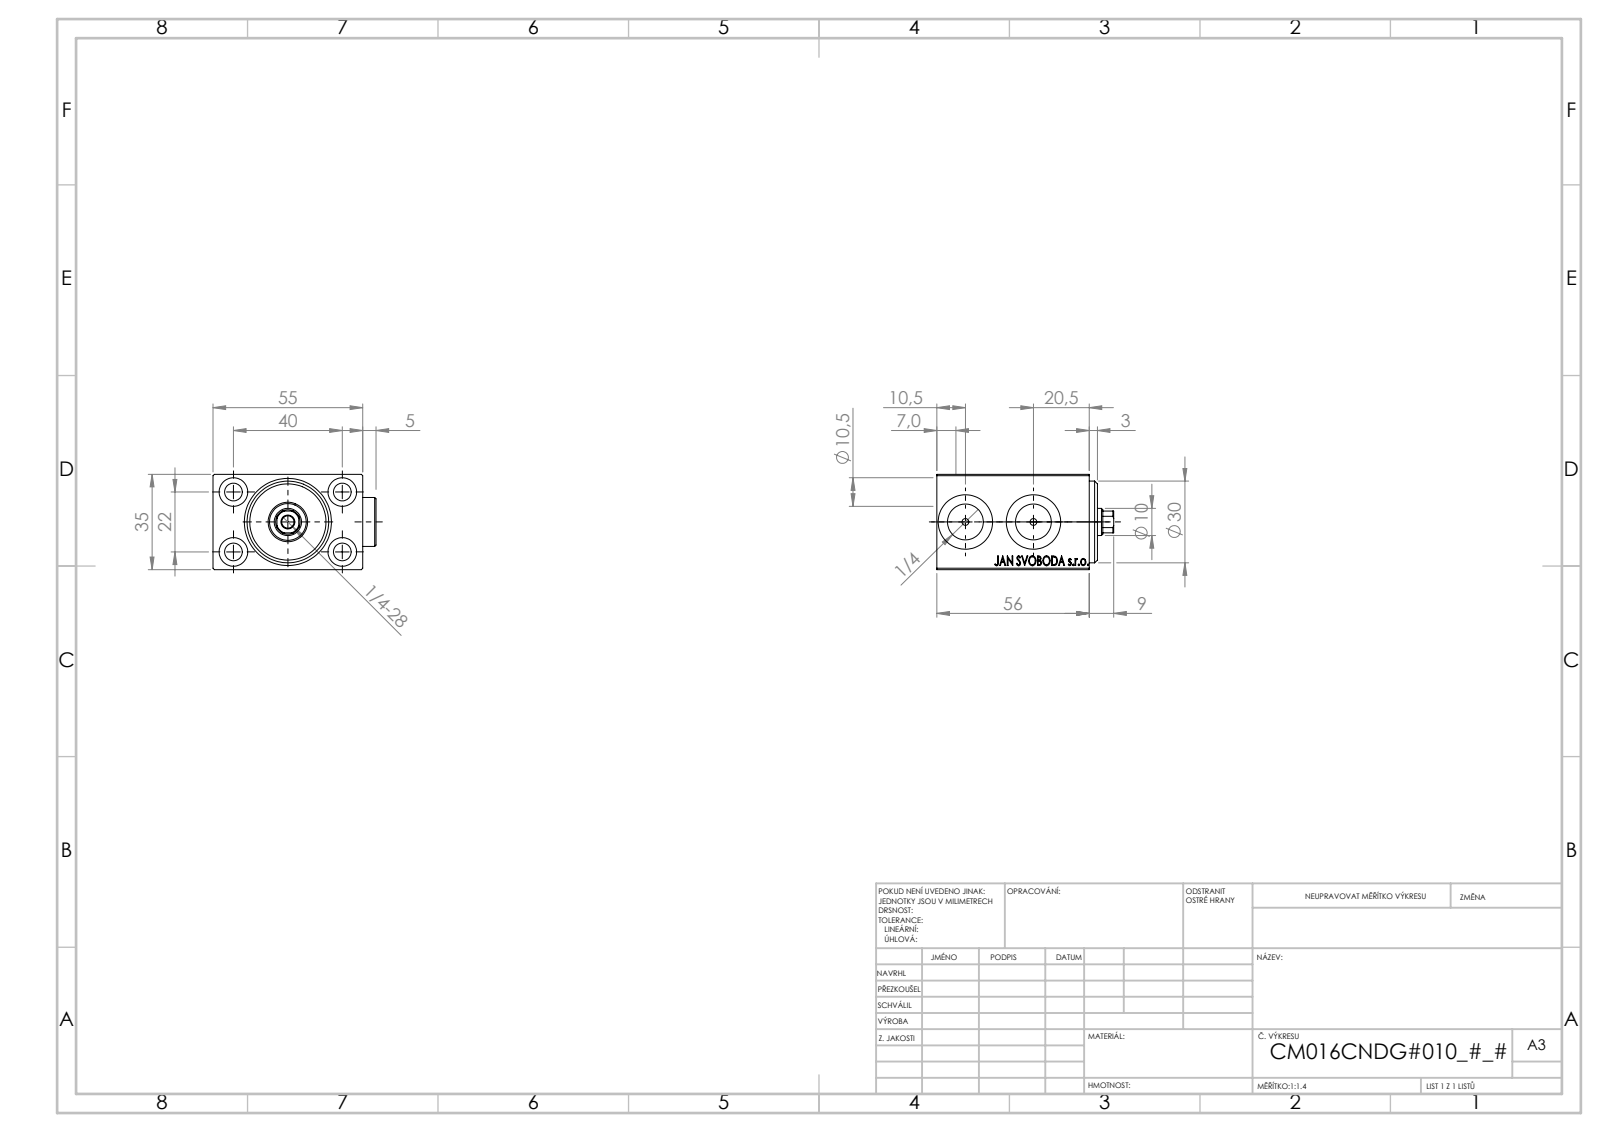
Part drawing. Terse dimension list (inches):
name: Zatka_OIL_PORT; V450CM_C_VCP; V450CM_VC_B; V450CM_C_Body
written by: SolidWorks 2019 (CONFIG_CONTROL_DESIGN)
unit: in
bodies: 5 solids, 919 faces (443 planar, 78 cylindrical, 398 other)
size: 2.559 × 2.358 × 1.378
volume: 5.689 in³; area: 48.64 in²
holes: 4× ⌀0.256, 4× ⌀0.413, 2× ⌀0.098, 2× ⌀0.518, 2× ⌀0.787, 1× ⌀0.177, 1× ⌀0.394, 1× ⌀0.531, 1× ⌀0.571, 1× ⌀0.63, 1× ⌀0.709, 1× ⌀1.181
bosses: 2× ⌀0.709
rounds: 1× R0.177
face distances: 1.378, 0.197, 2.008, 2.165, 2.161, 2.205, 0.079, 1.654, 0.118, 0.315
hole spacings: 0.899, 0.866, 1.575, 1.797, 0.984
